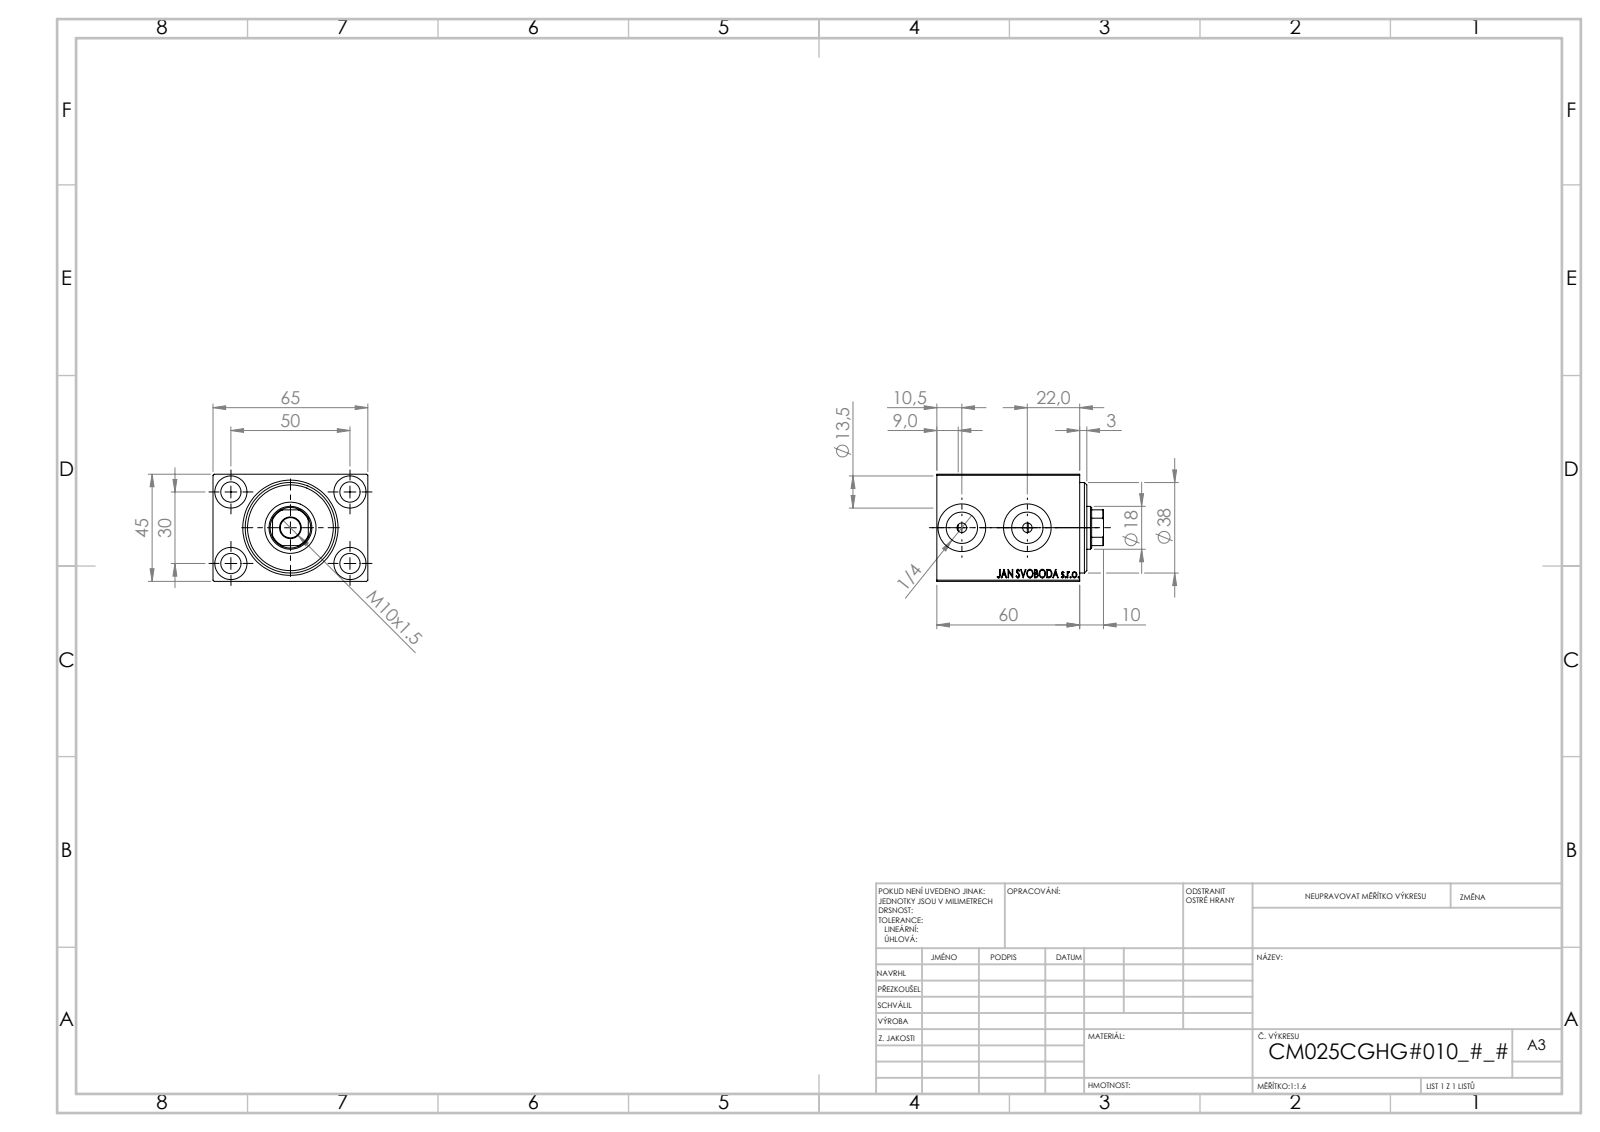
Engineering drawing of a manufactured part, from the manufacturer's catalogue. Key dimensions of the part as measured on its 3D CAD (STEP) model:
Part name (STEP PRODUCT): V450CM_VC_B; V450CM_C_Body; V450CM_C_VCP
STEP written by: SolidWorks 2019 (CONFIG_CONTROL_DESIGN)
Units: millimetres
Bodies: 3 solids, 863 faces (409 planar, 60 cylindrical, 394 other)
Overall size (bounding box): 70 × 65 × 45
Volume: 153 236 mm³ · Surface area: 42 342 mm²
Round holes (diameter × count): ⌀8.5 ×5, ⌀13.5 ×4, ⌀4 ×2, ⌀13.16 ×2, ⌀20 ×2, ⌀18 ×1, ⌀21.5 ×1, ⌀25 ×1, ⌀27 ×1, ⌀38 ×1
Partial cylindrical surfaces — rounded edges, fillets, slot ends (radius × count): R8.5 ×1
Main face-to-face distances: 45, 65, 9, 51, 5, 55, 46, 60, 8, 3
Hole centre spacings: 29.15, 30, 50, 58.31, 27.5
